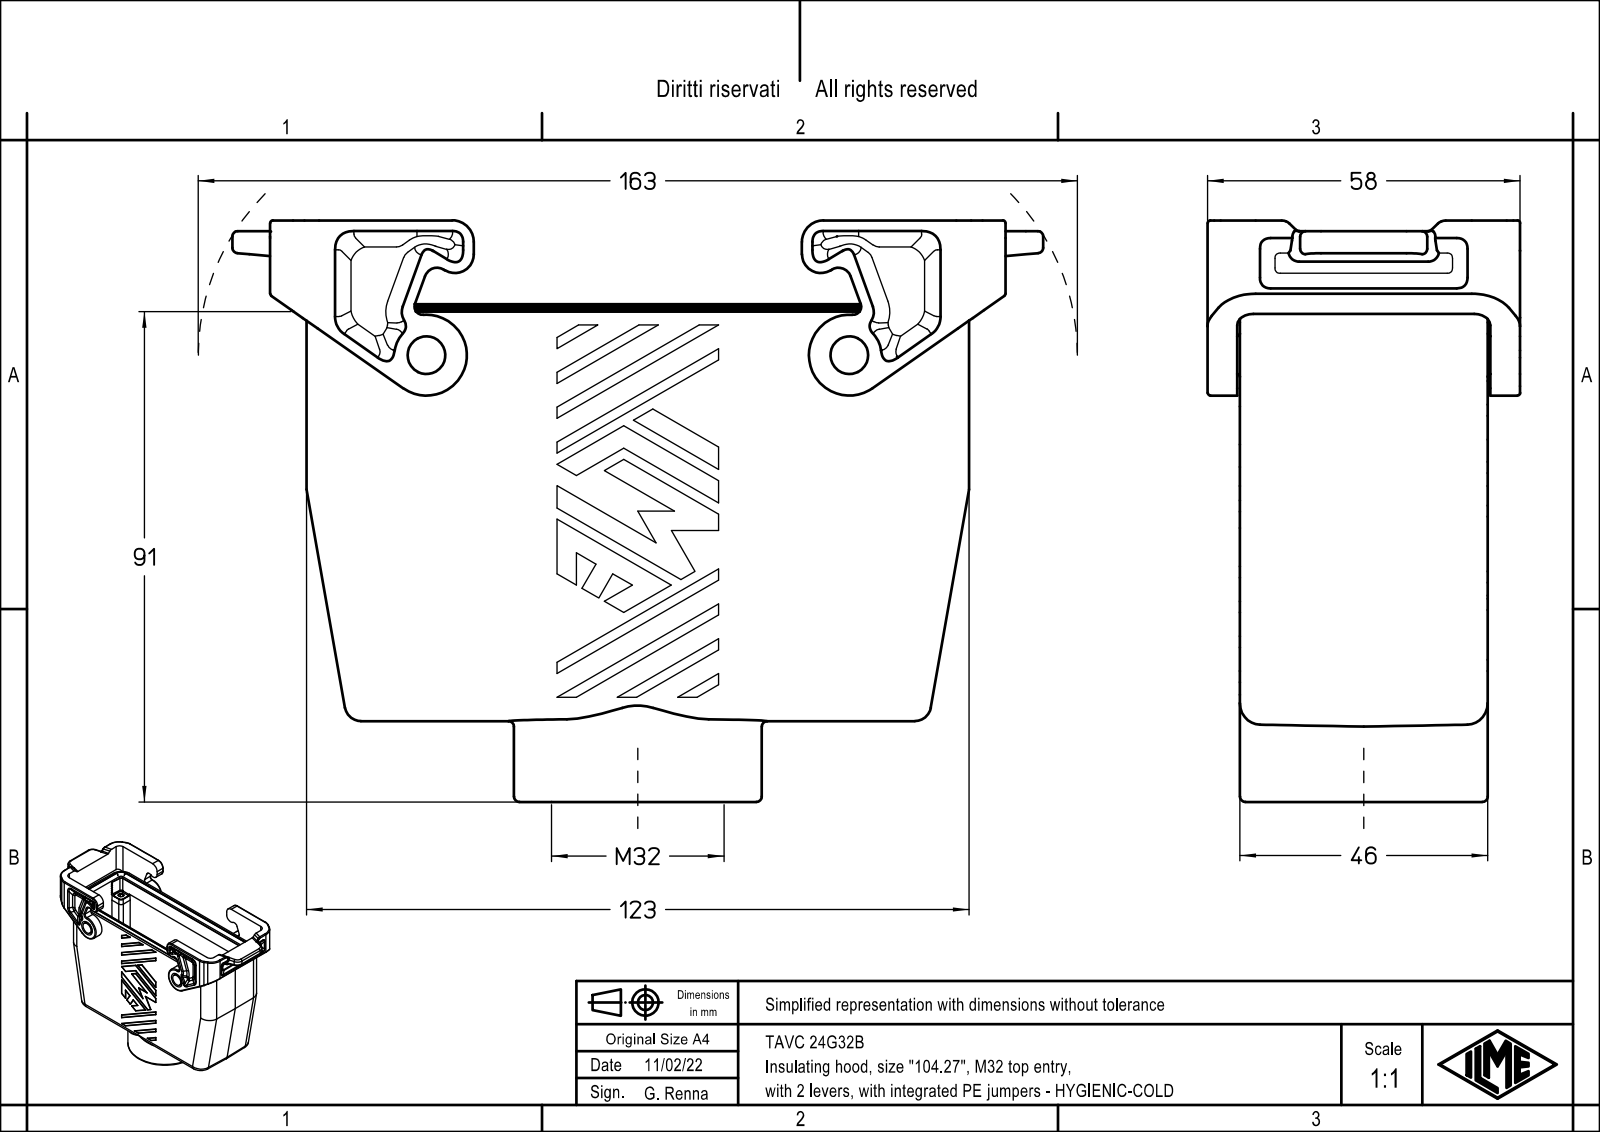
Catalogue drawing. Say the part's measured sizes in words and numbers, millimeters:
The part is named "TAVH 24 G32". Its 3-D file was written by "Creo Elements/Direct Modeling 20.1B 02-Apr-2019 (C) Parametric Technology GmbH (AUTOMOTIVE_DESIGN)". It is 1 solid with 754 faces: 374 planar, 318 cylindrical and 62 other. Overall it measures 150.5 by 107.9 by 58 millimeters. Its volume is 188 523 cubic millimeters and its surface area 75 803 square millimeters. Round holes: 4 of diameter 3.5, 1 of diameter 28, 1 of diameter 30.6. Round bosses or shafts: 2 of diameter 7, 1 of diameter 46. Partial cylindrical surfaces (rounded edges, fillets, slot ends): 88 of radius 0.15, 20 of radius 2, 20 of radius 3, 18 of radius 1.5, 16 of radius 1, 12 of radius 1.3, 8 of radius 6, 8 of radius 7. The main face-to-face distances are 5.4, 40.6, 35.2, 46, 5.9, 0.5, 41.1, 46.5, 34.8, 6.3. The hole center spacings are 53.72, 27, 104, 107.45.
